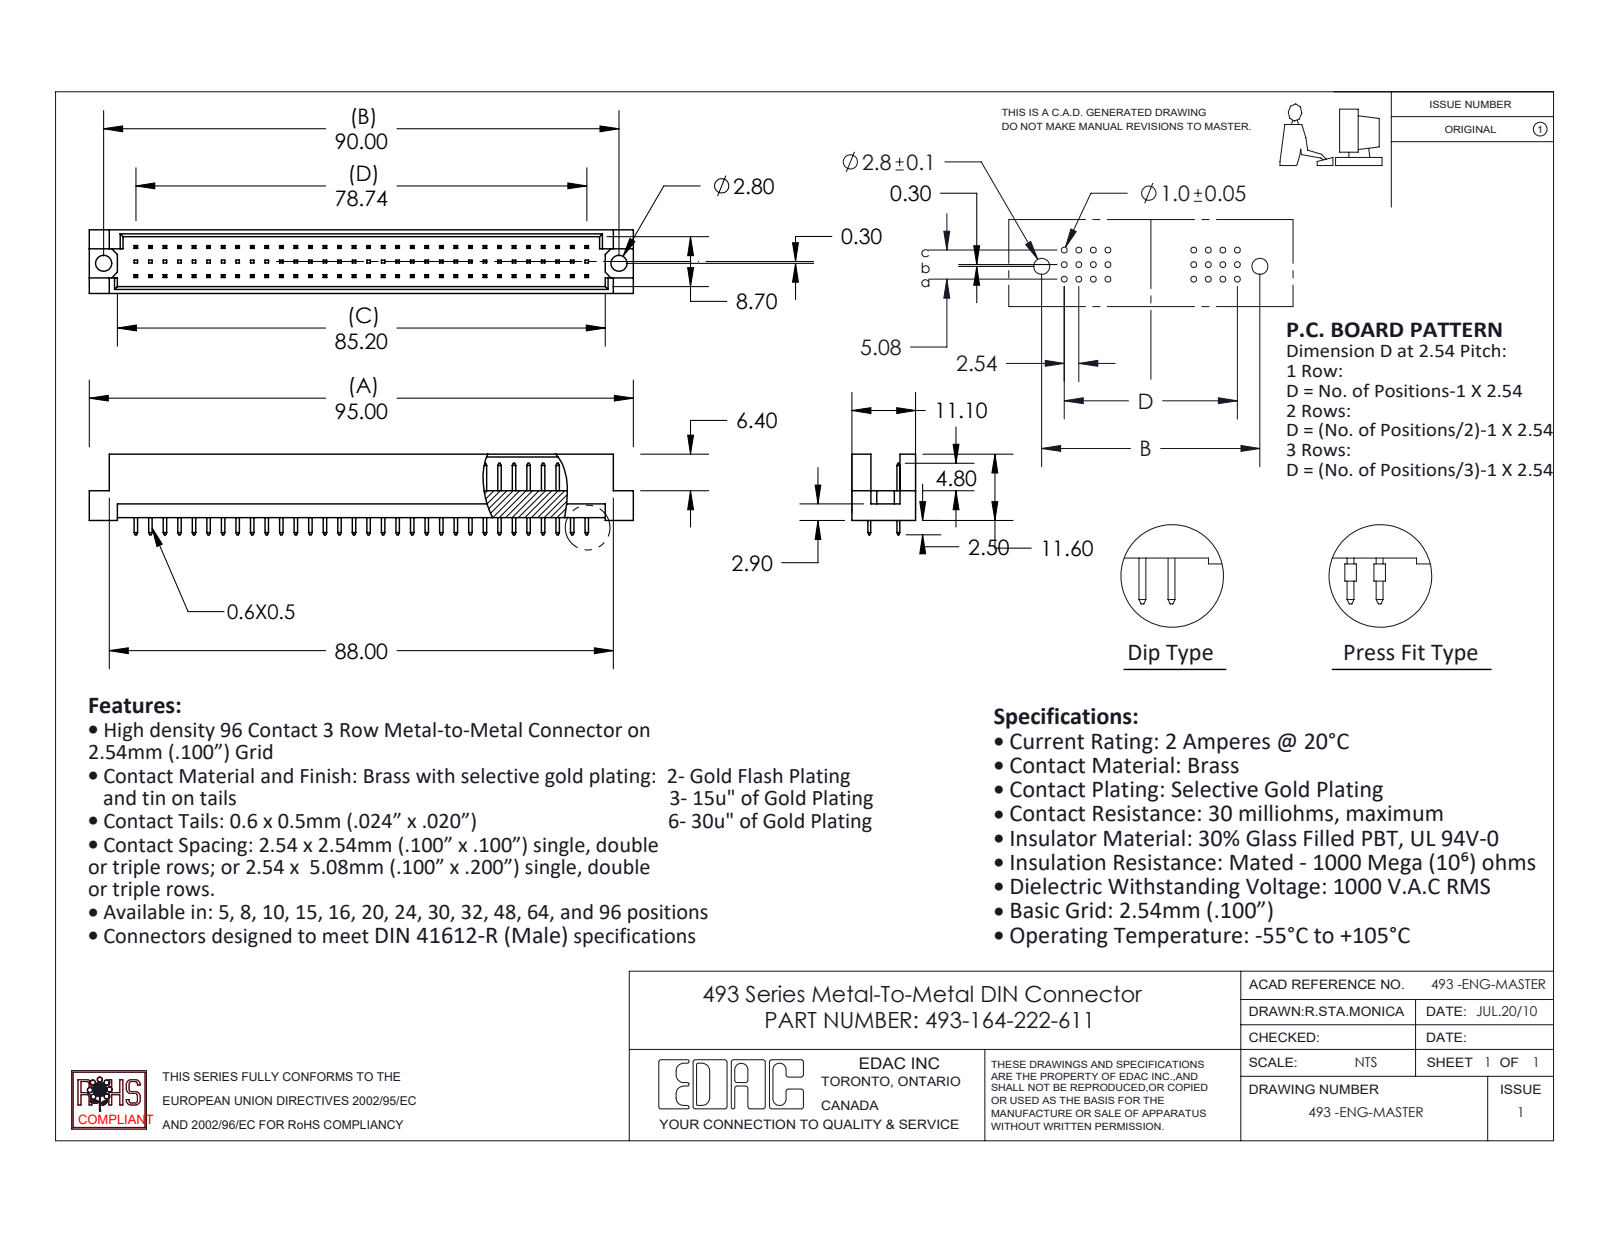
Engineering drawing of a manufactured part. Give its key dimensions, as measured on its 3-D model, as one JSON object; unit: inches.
{"part_name": "493-164-222-611; 493 Part_96; 493-290_22", "step_written_by": "SolidWorks 2020 (CONFIG_CONTROL_DESIGN)", "units": "inches", "bodies": {"solids": 65, "faces": 1332, "planar": 1328, "cylindrical": 4, "other": 0}, "overall_size": [3.74, 0.555, 0.437], "volume_in3": 0.36, "surface_area_in2": 12.73, "round_holes": [[0.11, 2]], "face_to_face_distances": [0.047, 0.39, 0.437, 0.2, 0.343, 0.02, 0.185, 0.109, 0.128, 0.309], "hole_center_spacings": [3.543]}
